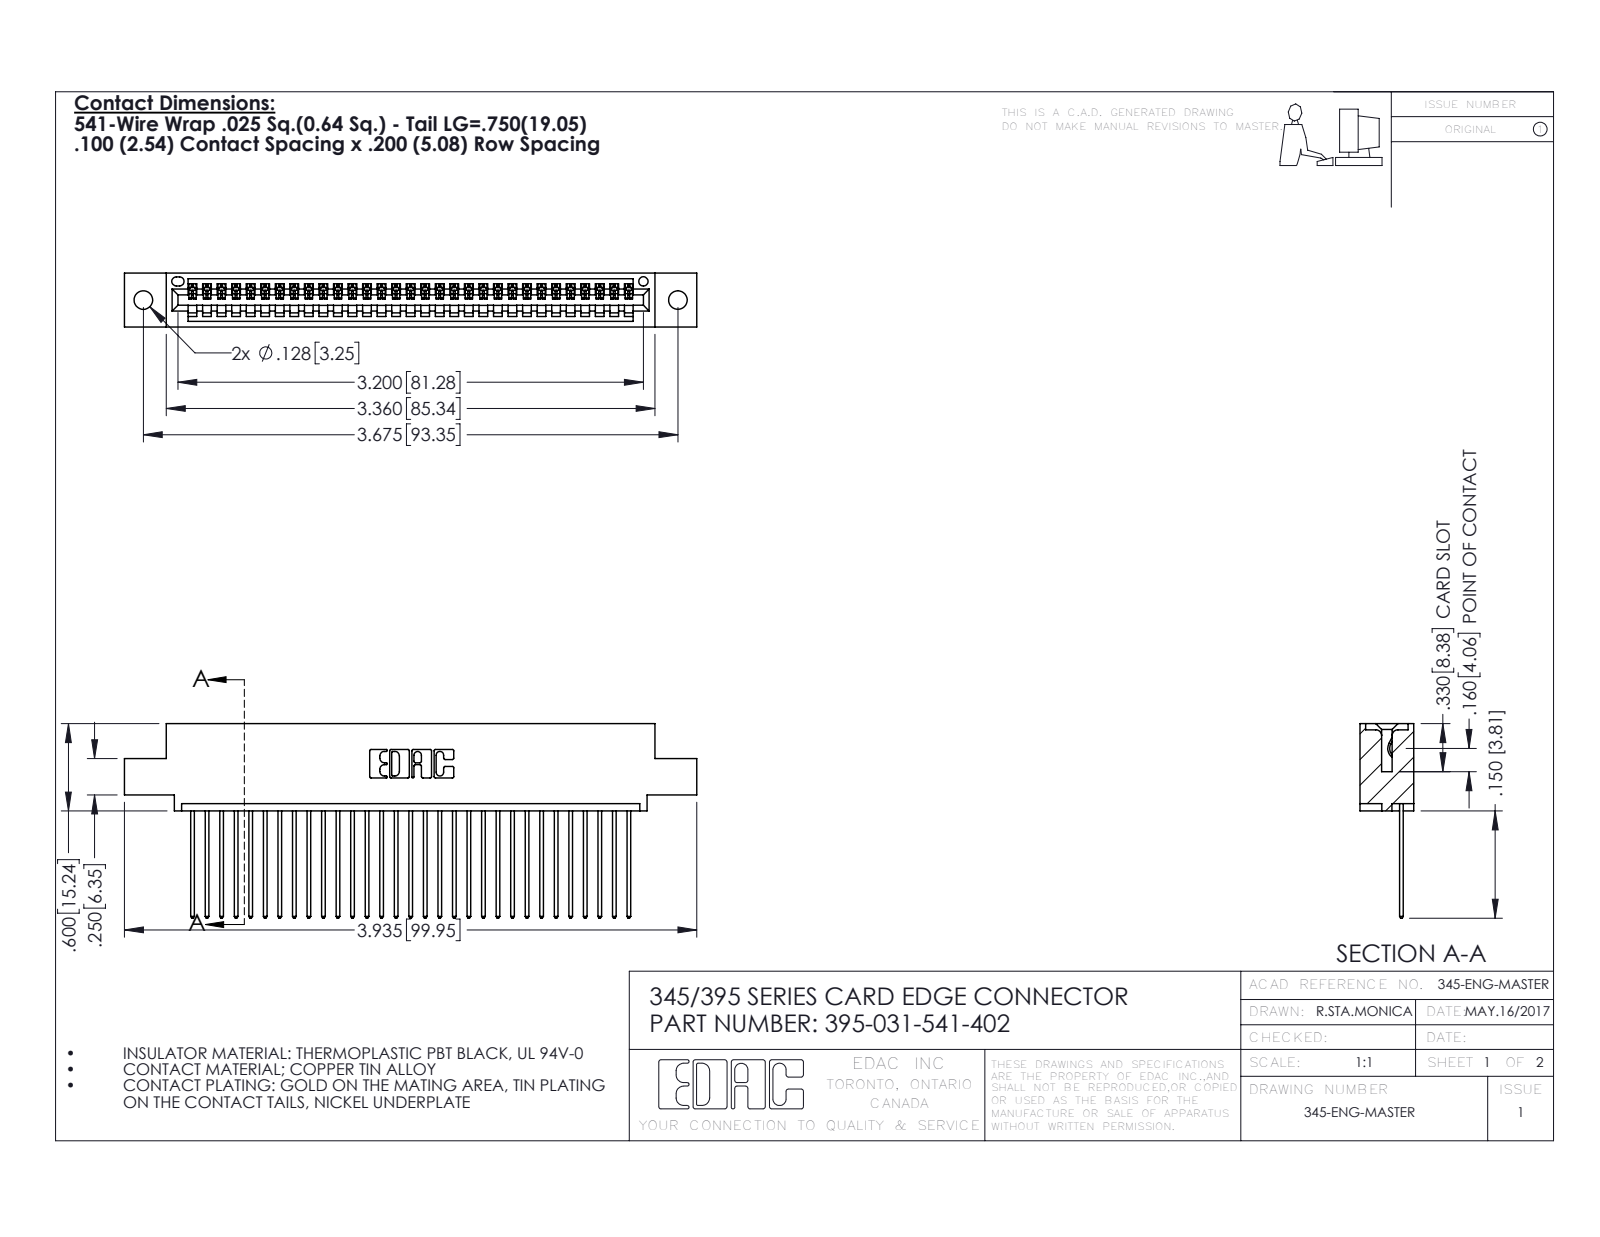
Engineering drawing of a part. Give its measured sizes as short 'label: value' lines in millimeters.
name: 345-292-001_345-293-141; 345 Part_0.110 Offset - 0.128 Dia; 395-031-541-402
written by: SolidWorks 2016 (CONFIG_CONTROL_DESIGN)
unit: mm
bodies: 32 solids, 1928 faces (1324 planar, 604 cylindrical, 0 other)
size: 99.9 × 34 × 9.4
volume: 9 390 mm³; area: 12 750 mm²
holes: 2× ⌀3.3, 1× ⌀1.6
rounds: 62× R0.2, 62× R0.3, 22× R0.3, 6× R0.2, 6× R0.8, 3× R0.7, 2× R0.8, 2× R1
face distances: 1.8, 7.6, 2.5, 6.9, 0.6, 9.4, 5.1, 5.7, 3.8, 1.8
hole spacings: 6.9, 87.4, 93.3
